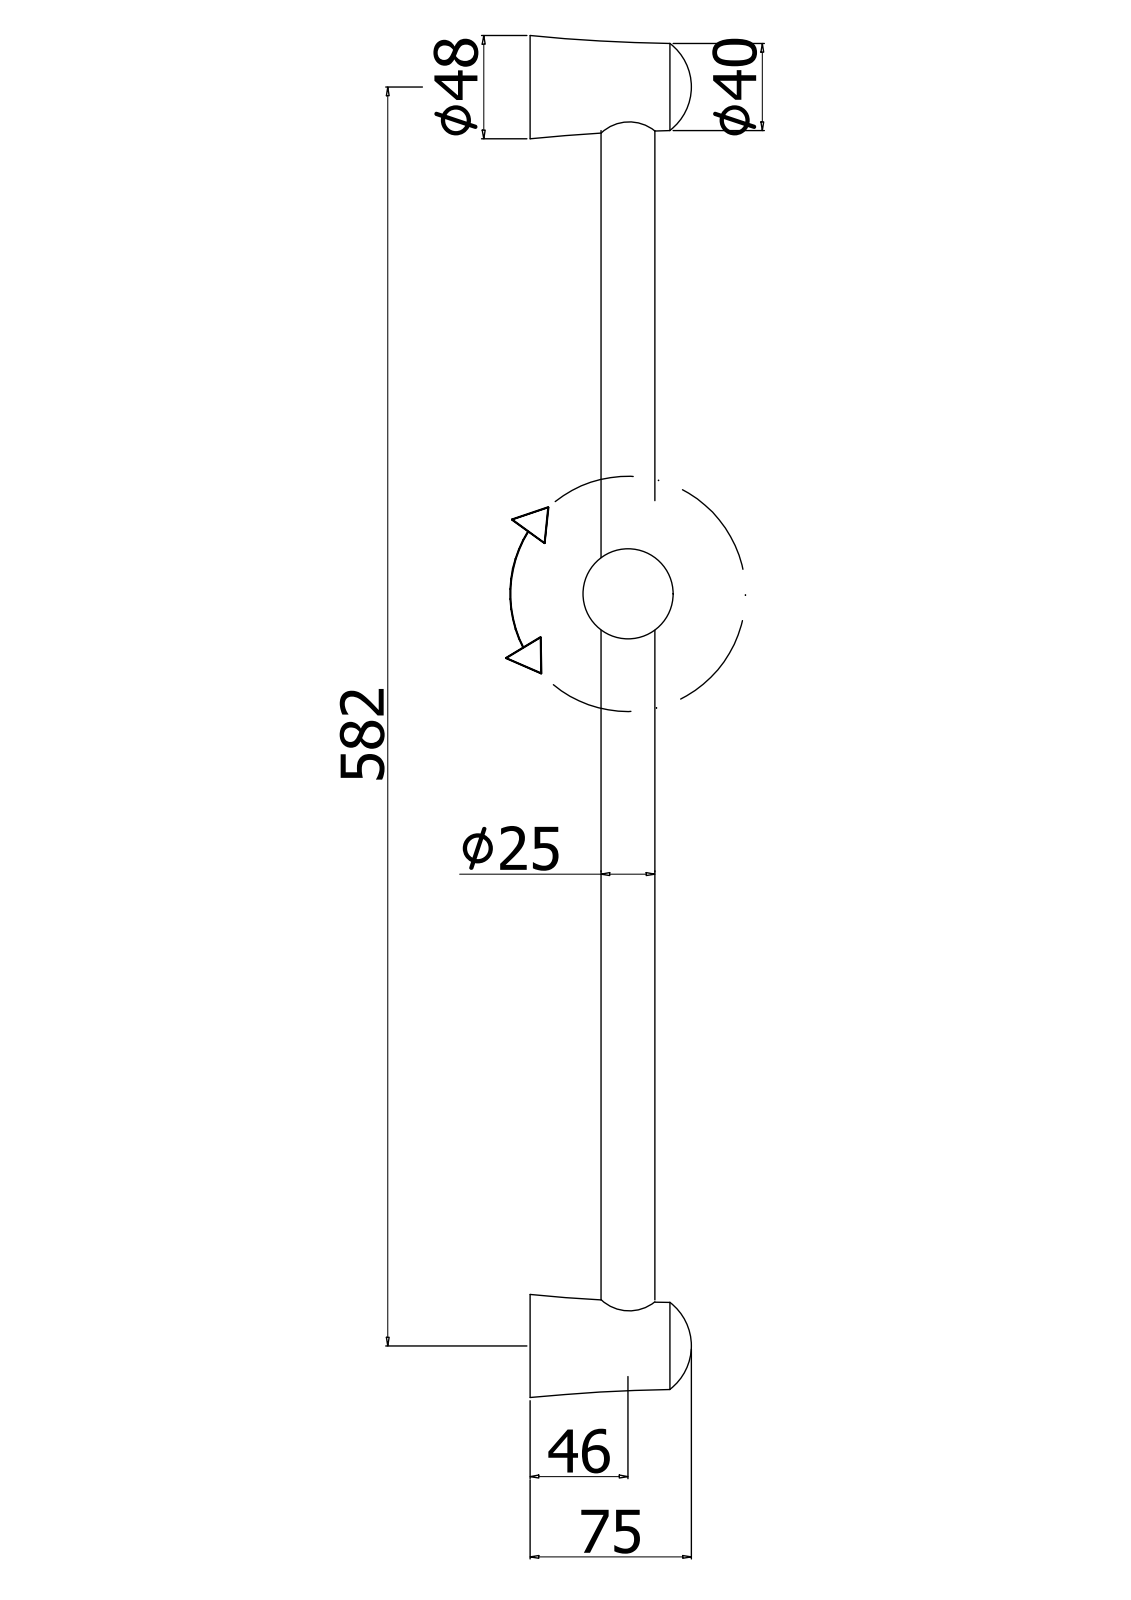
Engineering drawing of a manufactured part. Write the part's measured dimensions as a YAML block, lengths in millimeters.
part_name: "4071100CR"
step_written_by: "CREO PARAMETRIC BY PTC INC, 2020044 (CONFIG_CONTROL_DESIGN)"
units: millimeters
bodies: {solids: 1, faces: 101, planar: 14, cylindrical: 41, other: 46}
overall_size: [630, 123.46, 75]
volume: 329699
surface_area: 126839
round_holes:
  - {diameter: 4.5, count: 2}
  - {diameter: 23, count: 1}
round_bosses_or_shafts:
  - {diameter: 11, count: 2}
  - {diameter: 43, count: 1}
  - {diameter: 42.8, count: 1}
  - {diameter: 42.7, count: 1}
  - {diameter: 25, count: 1}
partial_cylinders:
  - {radius: 2, count: 12}
  - {radius: 11.5, count: 1}
face_to_face_distances: [28, 16, 1, 27, 39.15, 40.15, 39, 40]
hole_center_spacings: [582]
